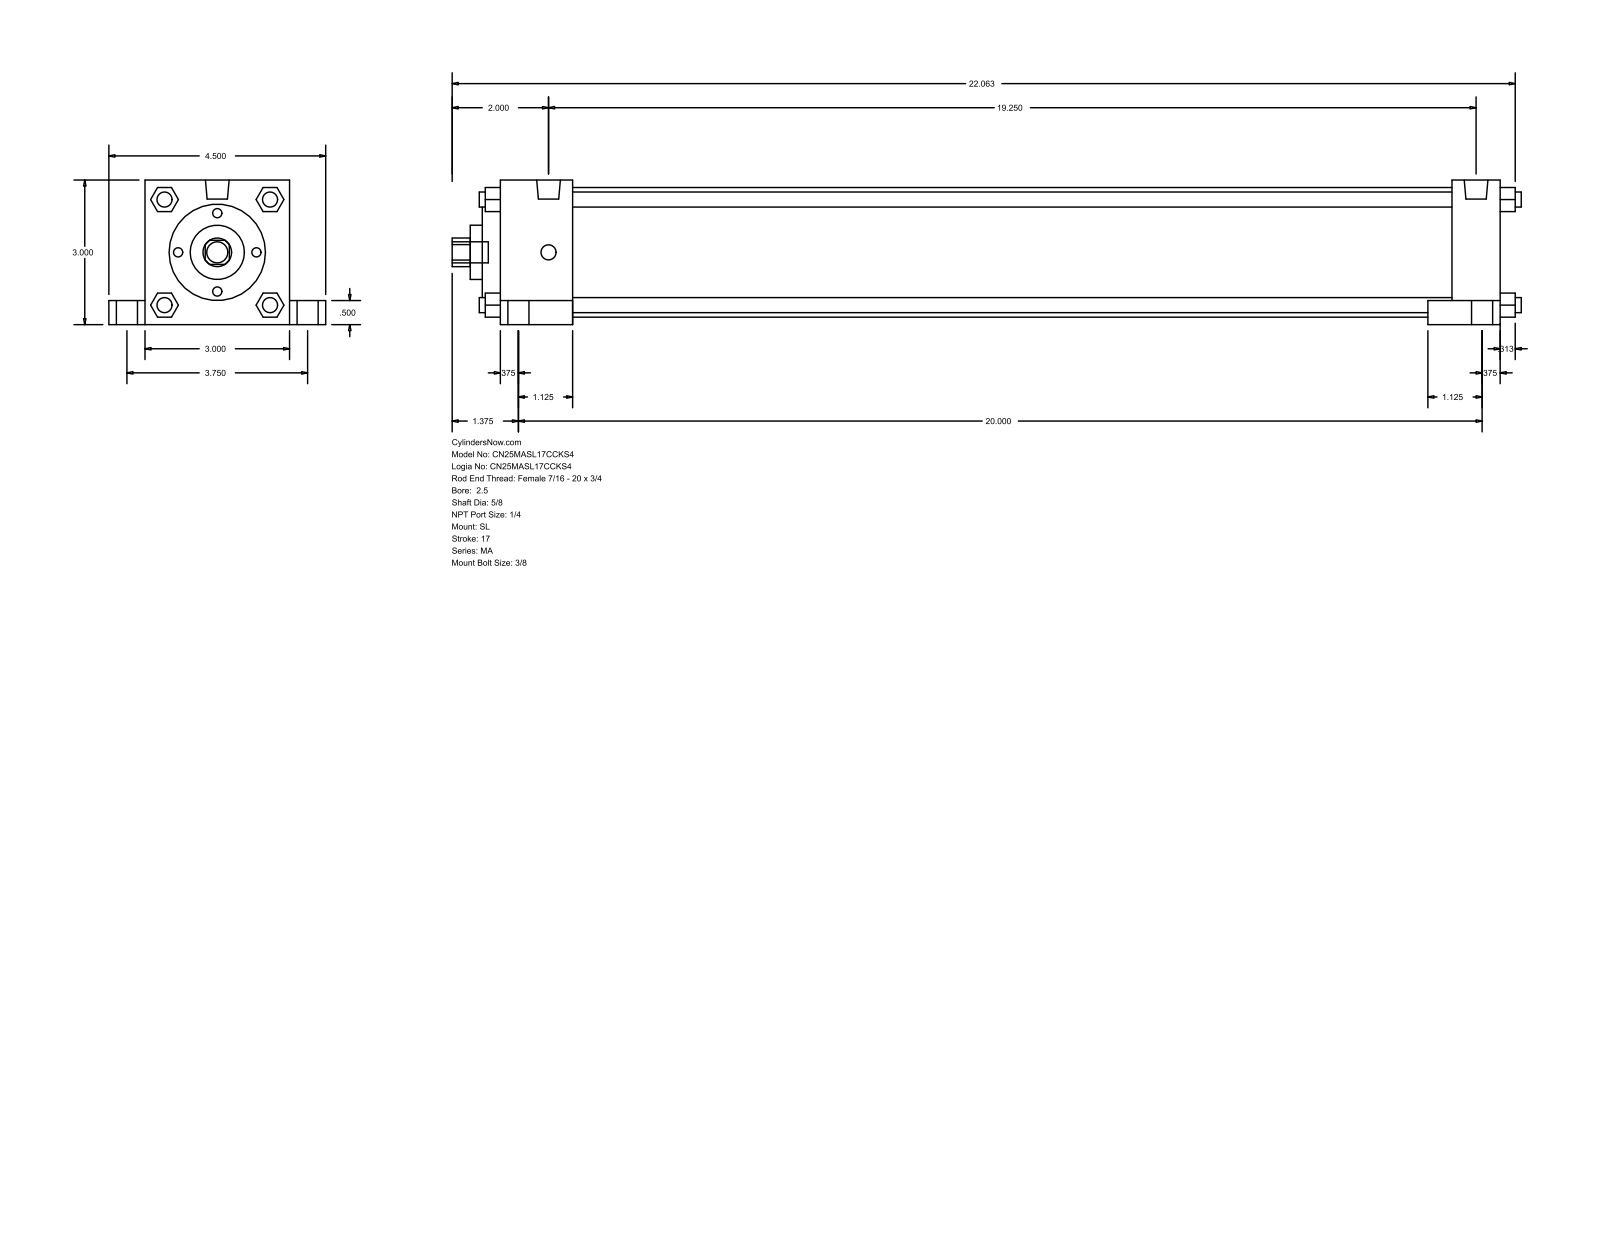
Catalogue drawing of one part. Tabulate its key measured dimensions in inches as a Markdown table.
| quantity | value |
| --- | --- |
| part name | MA_SL__0250_0.625 |
| STEP written by | GSSL Pune (CONFIG_CONTROL_DESIGN) |
| units | inches |
| bodies | 0 solids, 150 faces (113 planar, 37 cylindrical, 0 other) |
| overall size | 22.187 × 4.5 × 3 |
| round holes (diameter × count) | 0.625 × 1, 1.125 × 1, 2 × 1, 2.69 × 1 |
| round bosses / shafts (diameter × count) | 0.313 × 8, 0.437 × 5, 0.687 × 4, 0.492 × 2 |
| partial cylindrical surfaces (radius × count) | 0.297 × 1 |
| main face-to-face distances | 3, 20.75, 0.5, 18.25, 1, 1.5, 19.25, 19.75, 0.75, 2.5 |
